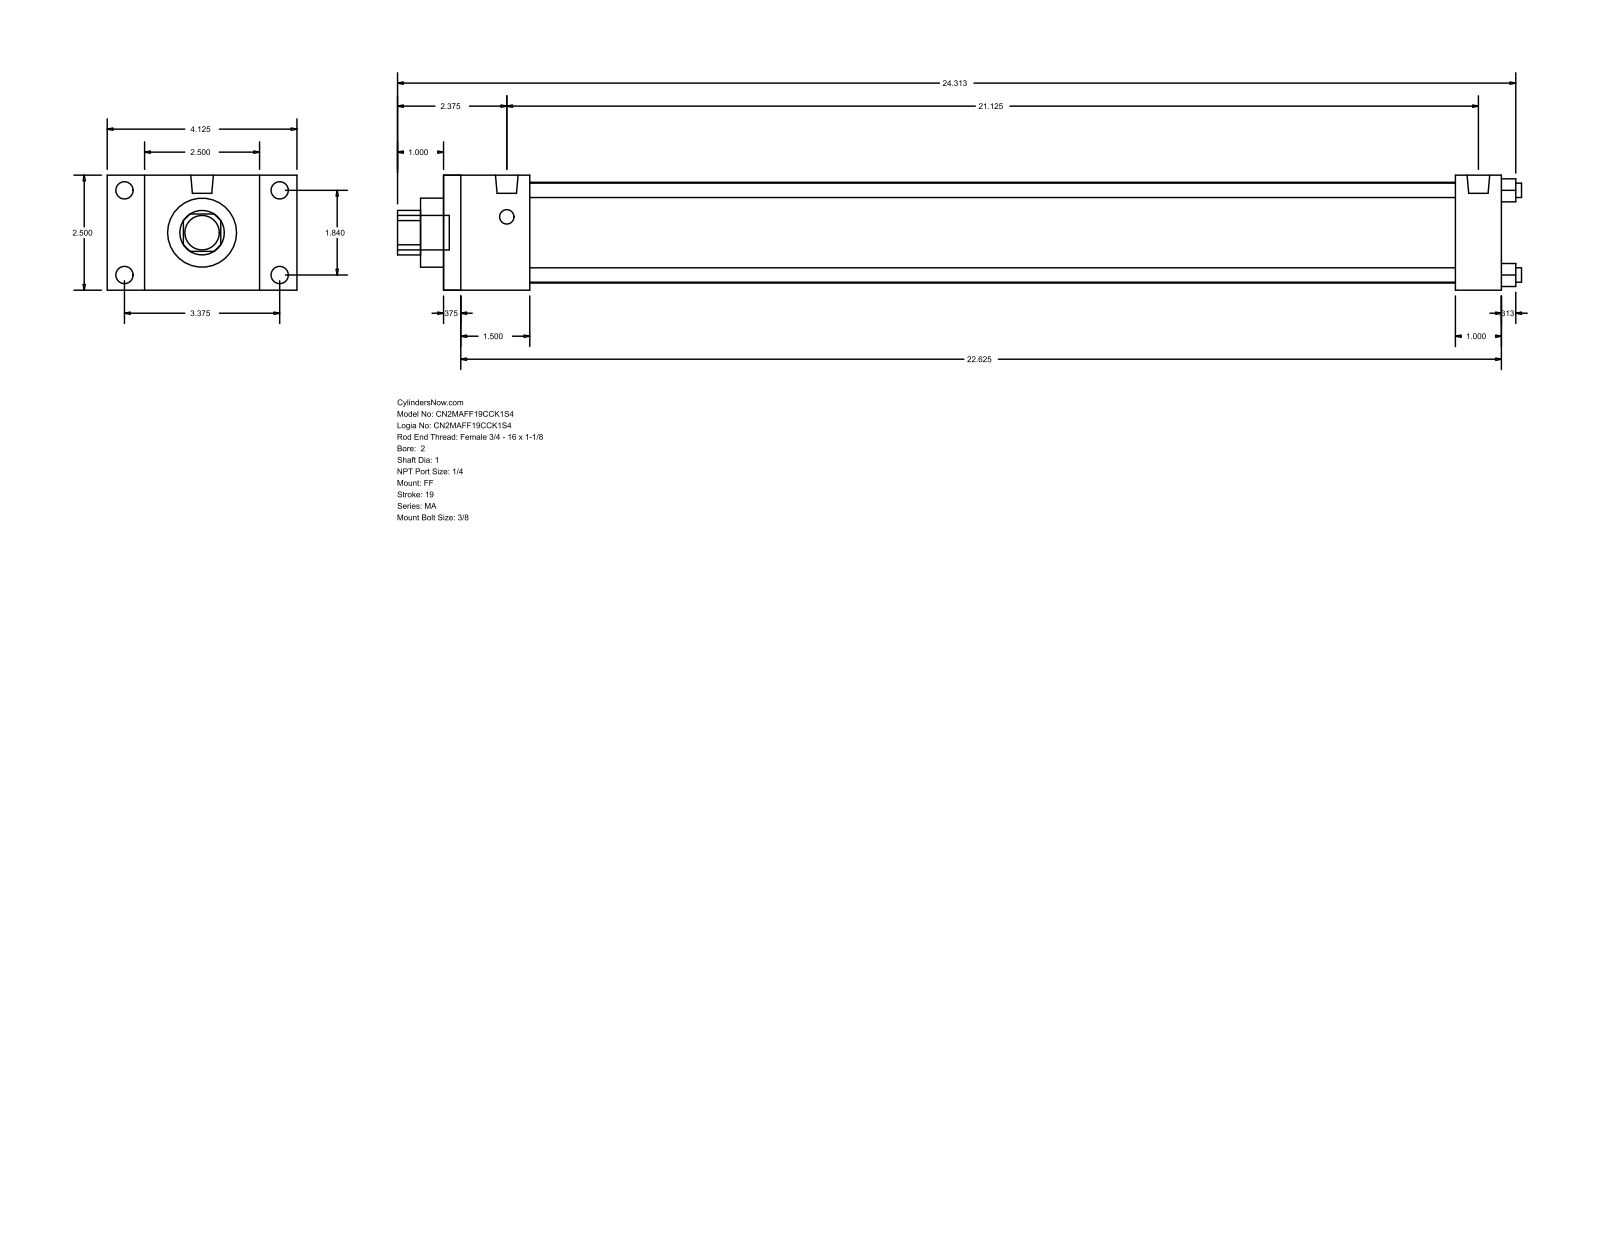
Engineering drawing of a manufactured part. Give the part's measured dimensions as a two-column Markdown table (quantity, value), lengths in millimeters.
| quantity | value |
| --- | --- |
| part name | MA_FF__0200_1 |
| STEP written by | GSSL Pune (CONFIG_CONTROL_DESIGN) |
| units | millimeters |
| bodies | 0 solids, 92 faces (64 planar, 28 cylindrical, 0 other) |
| overall size | 620.71 × 104.78 × 63.5 |
| round holes (diameter × count) | 7.94 × 4, 25.4 × 1, 38.1 × 1, 55.63 × 1 |
| round bosses / shafts (diameter × count) | 9.53 × 4, 7.94 × 4, 12.49 × 2, 19.05 × 1 |
| partial cylindrical surfaces (radius × count) | 12.29 × 1 |
| main face-to-face distances | 63.5, 584.2, 9.52, 574.68, 25.4, 20.64, 12.7, 47.63, 558.8, 38.11 |
| hole center spacings | 33.05, 46.74, 66.1 |
